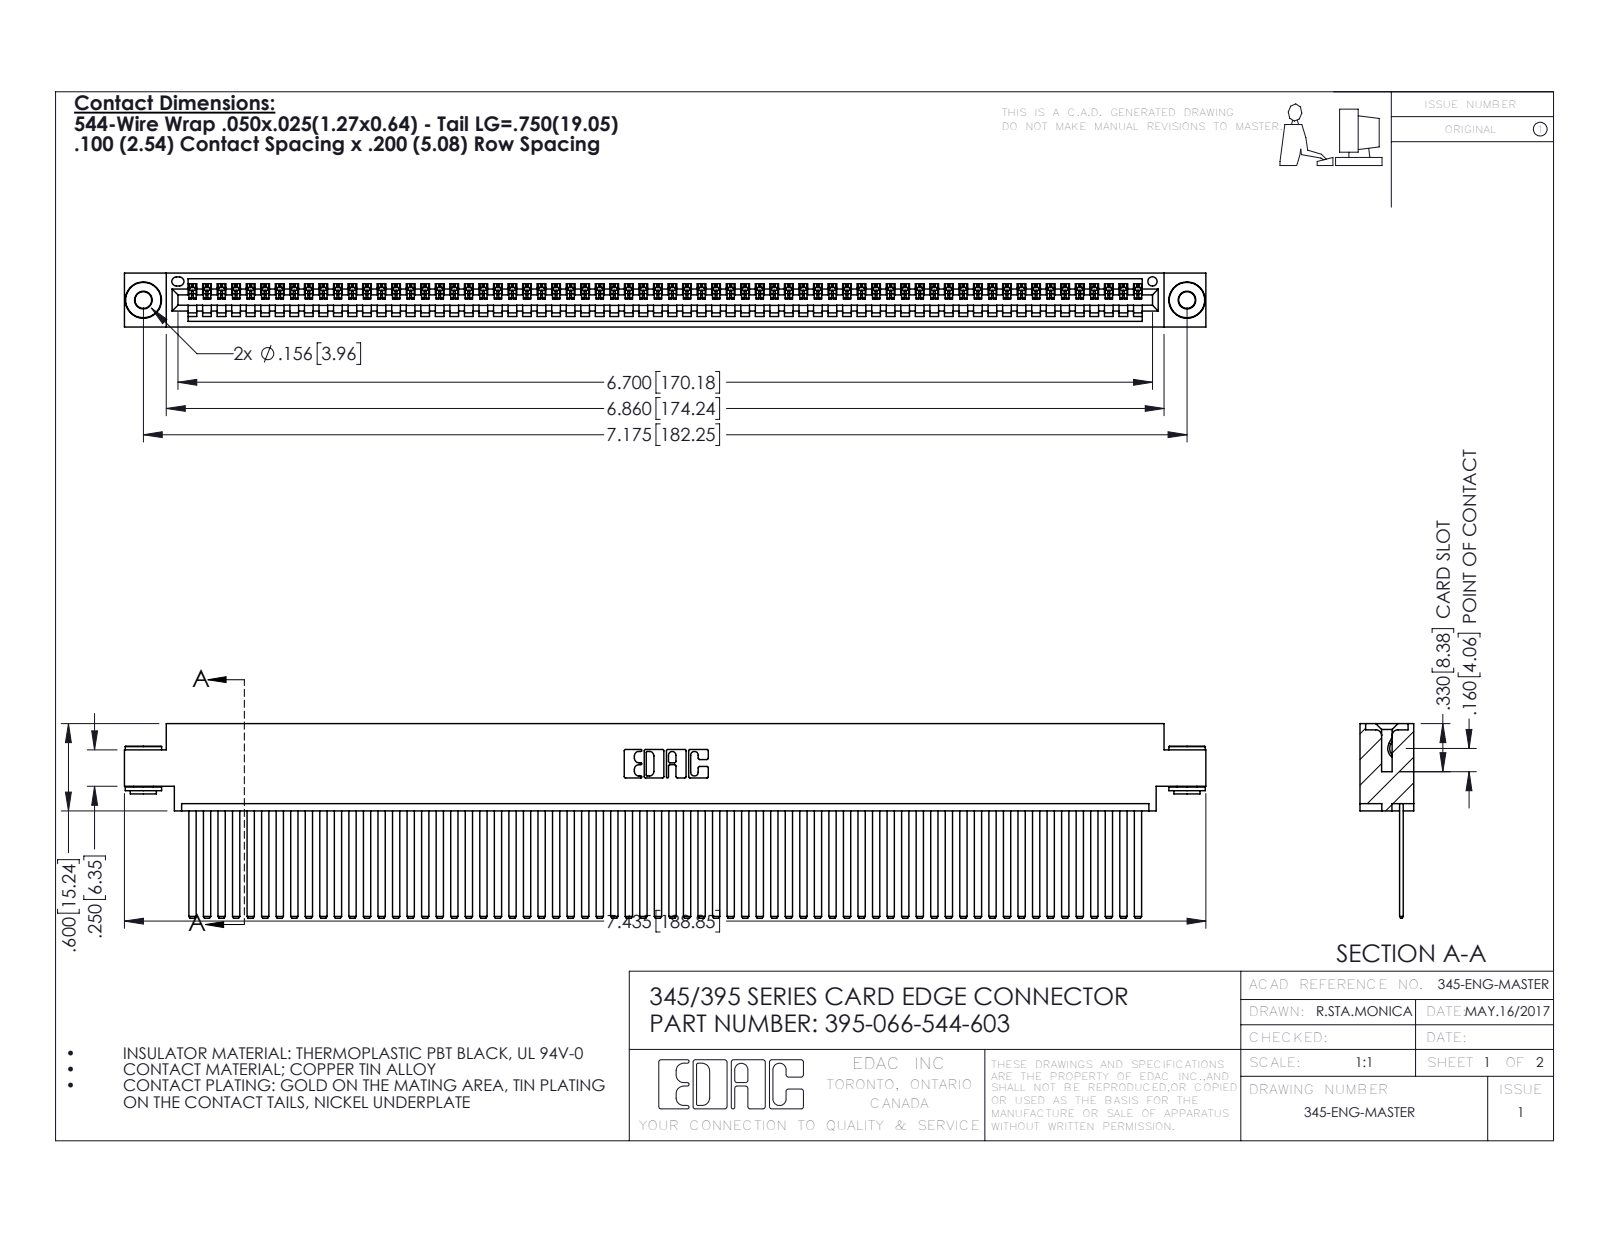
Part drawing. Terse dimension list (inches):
name: 395-066-544-603; 345-250-002_345-250-002-102; 345-292-001_345-293-144; 345 Part_0.170 Offset - 0.156 Dia-TH
written by: SolidWorks 2016 (CONFIG_CONTROL_DESIGN)
unit: in
bodies: 69 solids, 3600 faces (2470 planar, 1122 cylindrical, 8 other)
size: 7.435 × 1.337 × 0.37
volume: 1.147 in³; area: 43.32 in²
holes: 2× ⌀0.116, 2× ⌀0.156, 1× ⌀0.064
bosses: 2× ⌀0.25, 2× ⌀0.18, 2× ⌀0.136
rounds: 132× R0.006, 22× R0.01, 6× R0.007, 6× R0.031, 3× R0.026, 2× R0.031, 2× R0.04, 1× R0.014
face distances: 0.072, 0.298, 0.025, 0.098, 0.272, 0.37, 0.2, 0.225, 0.175, 0.149
hole spacings: 0.27, 6.939, 7.175
